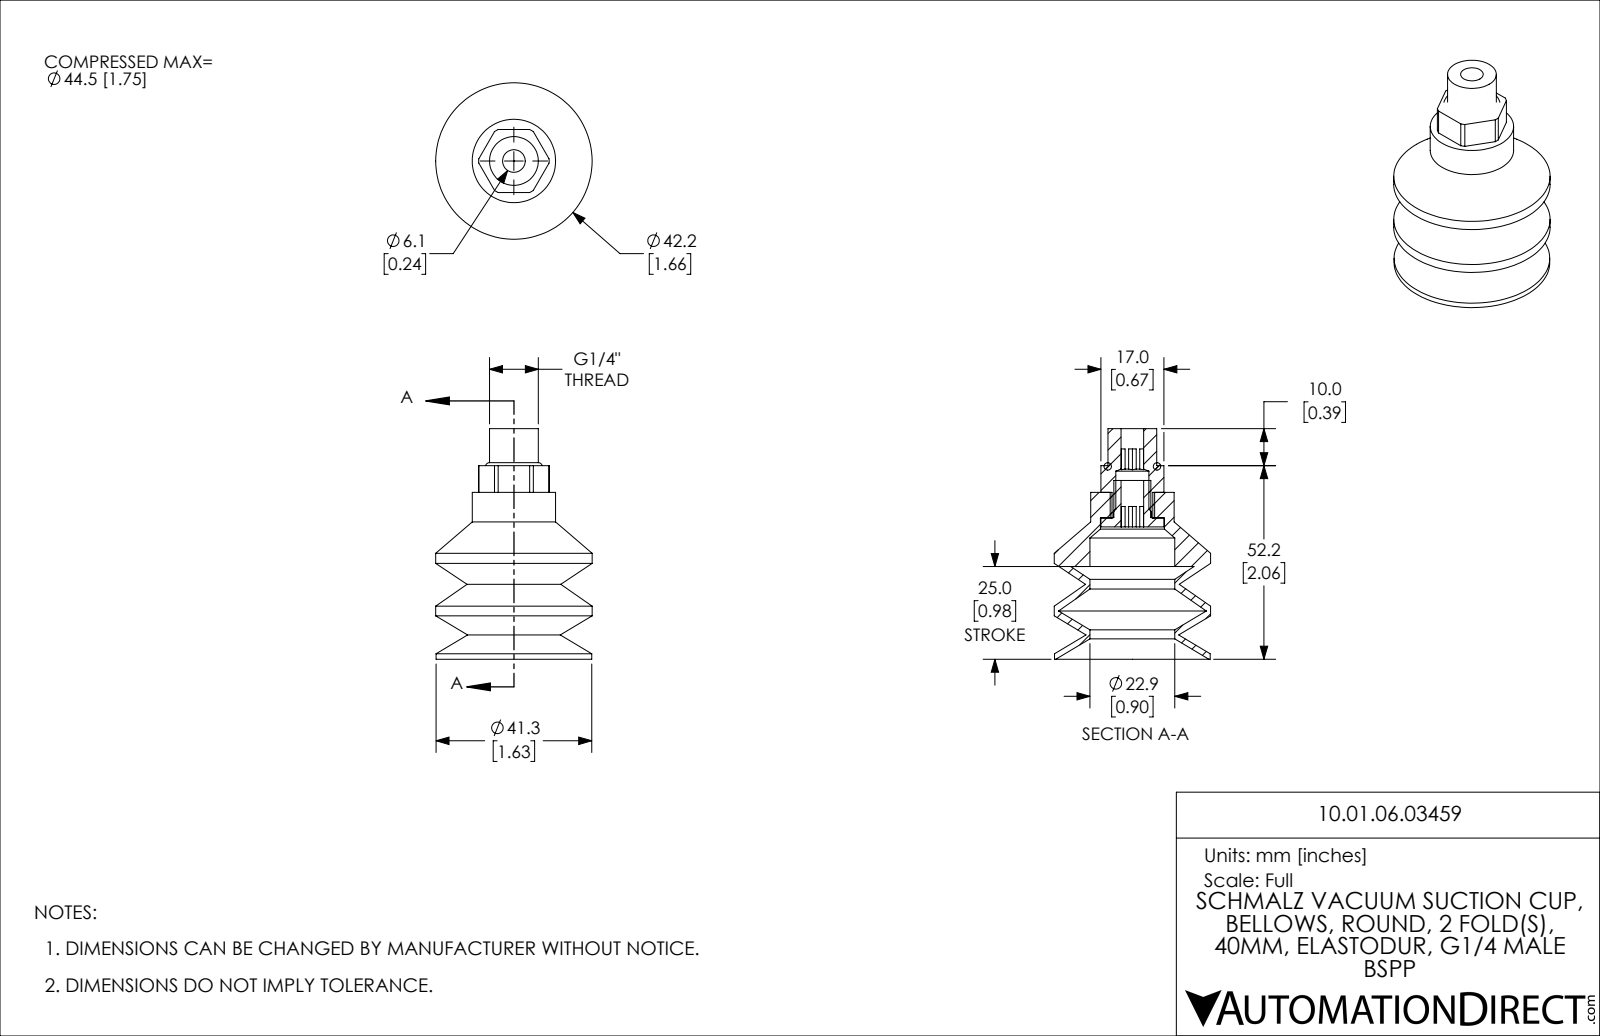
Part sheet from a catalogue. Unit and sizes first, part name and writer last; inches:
Units: inches
Overall size (bounding box): 2.449 × 1.661 × 1.661
Round holes (diameter × count): ⌀0.24 ×1, ⌀0.351 ×1, ⌀0.402 ×1, ⌀0.433 ×1, ⌀0.681 ×1, ⌀0.902 ×1
Round bosses / shafts (diameter × count): ⌀1.661 ×1, ⌀1.654 ×1, ⌀0.886 ×1, ⌀0.669 ×1, ⌀0.518 ×1, ⌀0.472 ×1, ⌀0.394 ×1
Partial cylindrical surfaces — rounded edges, fillets, slot ends (radius × count): R0.374 ×1
Main face-to-face distances: 0.787, 0.421, 0.366, 0.669, 0.52, 0.098, 0.268, 0.551, 0.217, 0.394
Volume: 1.26 in³ · Surface area: 25.76 in²
Bodies: 4 solids, 122 faces (53 planar, 41 cylindrical, 28 other)
Part name (STEP PRODUCT): 10.01.06.03459
STEP written by: SolidWorks 2021 (CONFIG_CONTROL_DESIGN)
